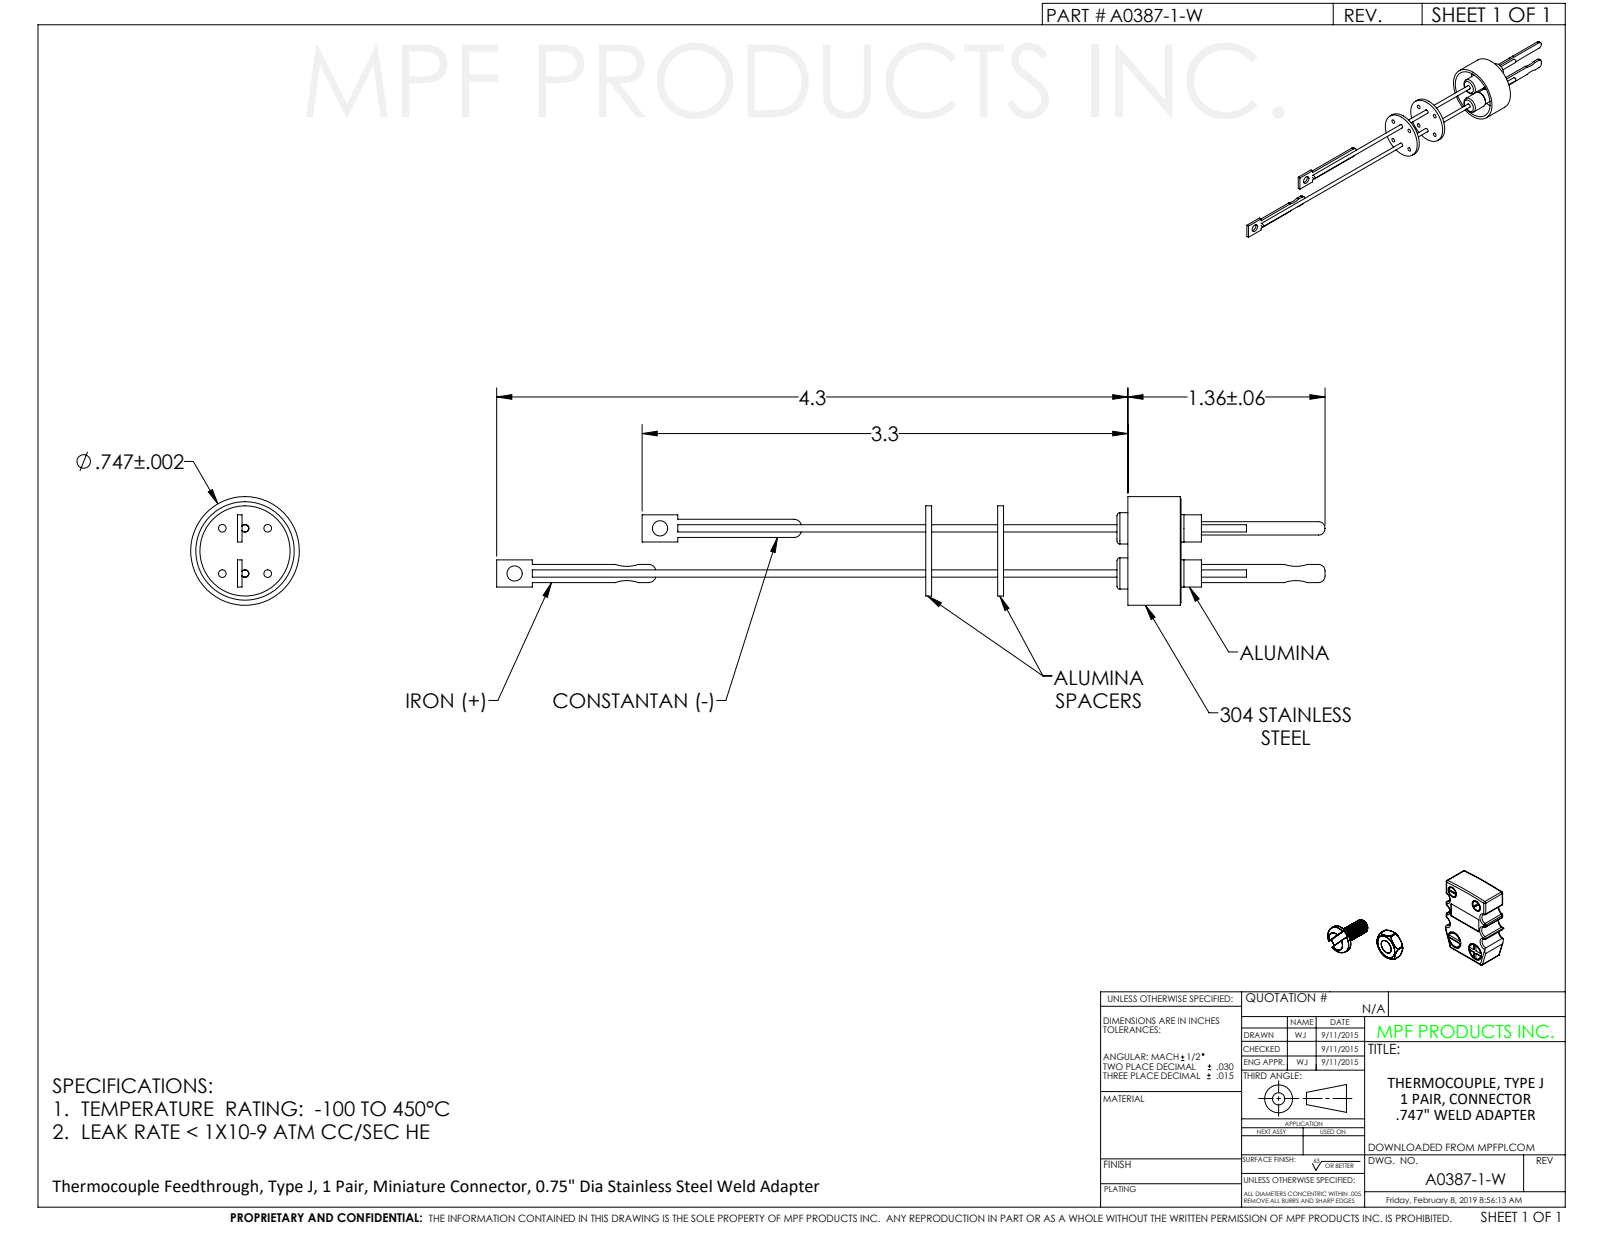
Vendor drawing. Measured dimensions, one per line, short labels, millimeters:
name: A0387-1-W
written by: SolidWorks 2011 (CONFIG_CONTROL_DESIGN)
unit: mm
bodies: 1 solid, 140 faces (59 planar, 72 cylindrical, 9 other)
size: 145.2 × 19 × 19
volume: 2 150 mm³; area: 4 537 mm²
holes: 1× ⌀2.6, 1× ⌀3.1, 1× ⌀17.4, 1× ⌀18.2
bosses: 2× ⌀5.5, 2× ⌀5.1, 2× ⌀1.3, 1× ⌀19, 1× ⌀18.1, 1× ⌀15.7
rounds: 4× R0.8, 2× R1.3, 2× R6.2, 1× R0.6, 1× R1.2, 1× R1.7, 1× R2
face distances: 1, 13.5, 1.3, 0.8, 14.6, 54.8, 56.1, 12.5, 53.8, 55
hole spacings: 3.9, 7.9, 26
